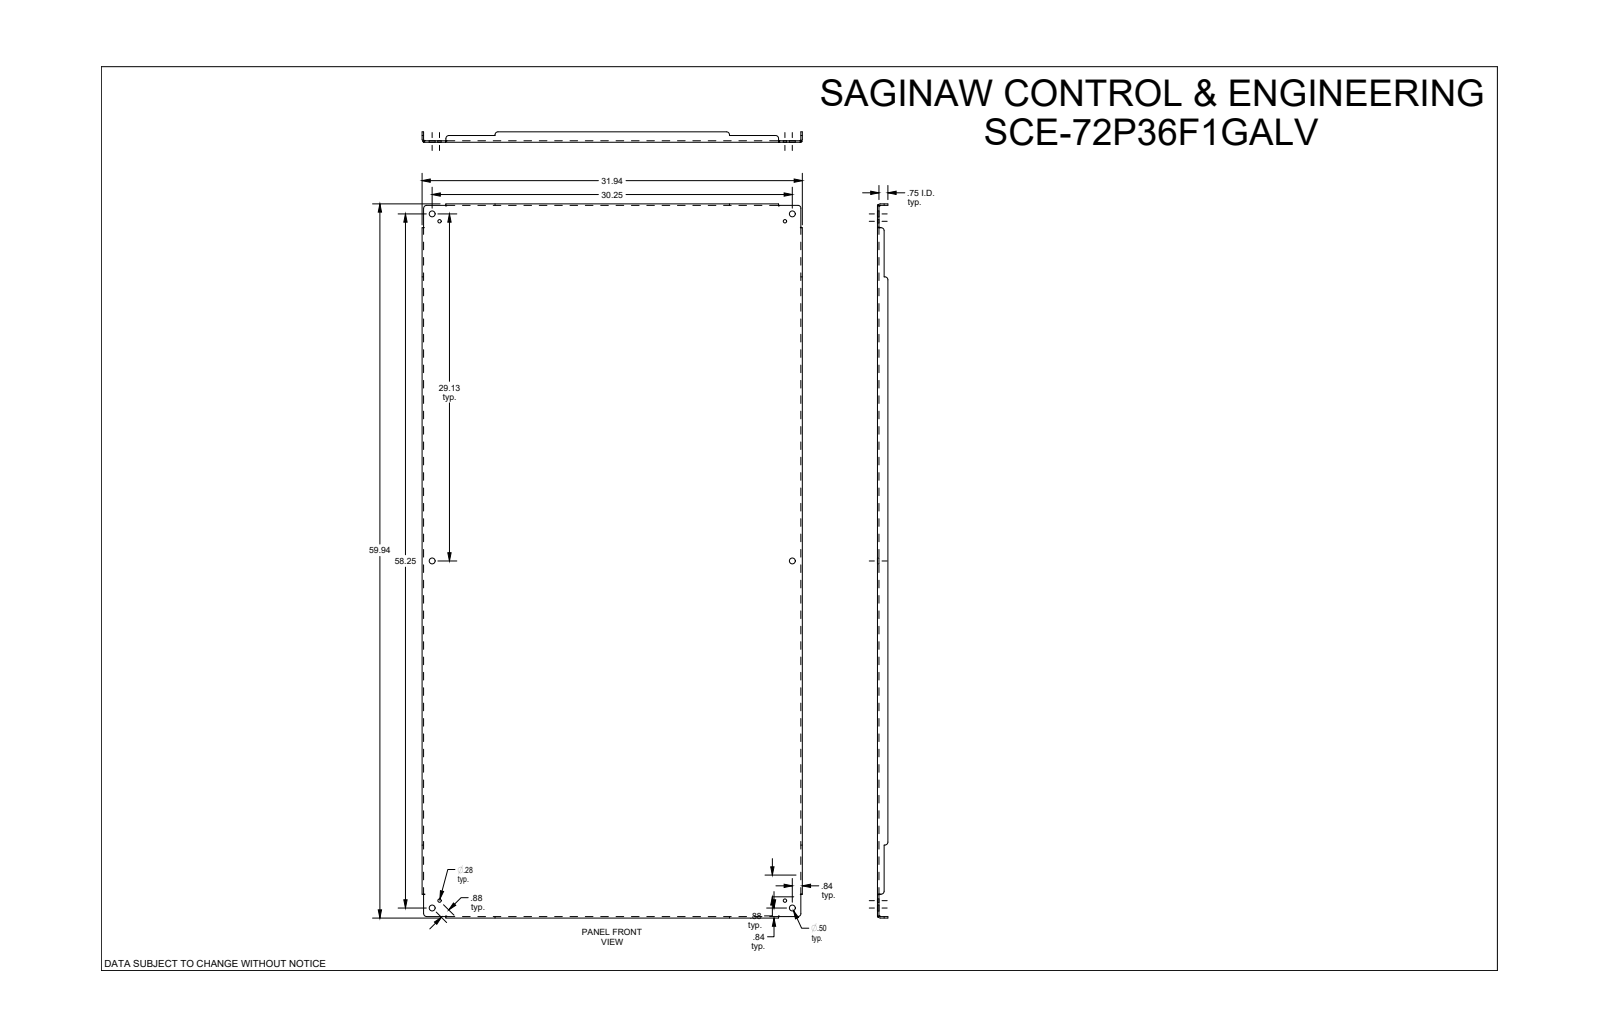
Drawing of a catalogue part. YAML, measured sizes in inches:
part_name: "SCE-72P36F1GALV"
step_written_by: "SolidWorks 2019 (CONFIG_CONTROL_DESIGN)"
units: inches
bodies: {solids: 1, faces: 108, planar: 46, cylindrical: 38, other: 24}
overall_size: [59.938, 31.938, 0.875]
volume: 251.7
surface_area: 4052
round_holes:
  - {diameter: 0.5, count: 6}
  - {diameter: 0.281, count: 4}
partial_cylinders:
  - {radius: 0.25, count: 12}
  - {radius: 0.112, count: 4}
  - {radius: 0.237, count: 4}
face_to_face_distances: [0.125, 0.125, 31.813, 31.687, 31.938, 59.813, 0.75, 0.875, 59.687, 59.938]
hole_center_spacings: [0.875, 28.513, 29.125, 29.637, 41.117, 41.992, 57.634, 64.802]
